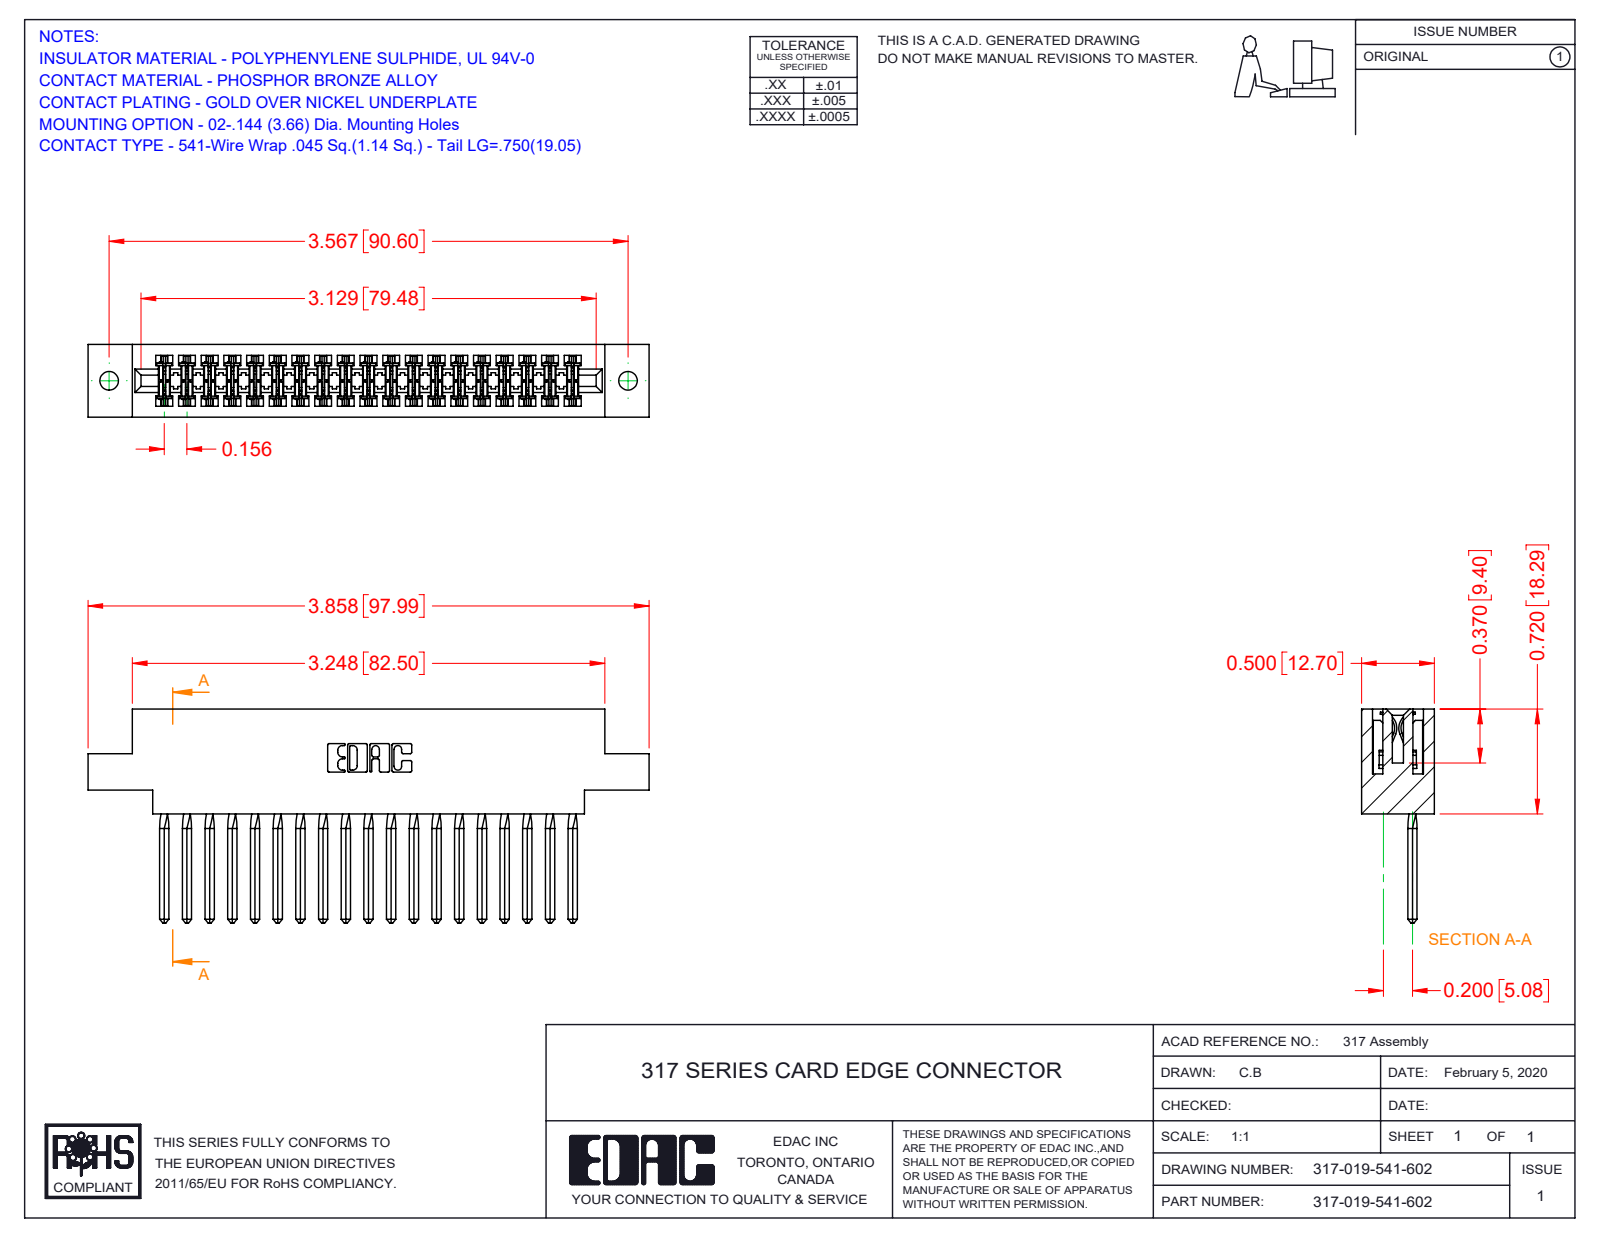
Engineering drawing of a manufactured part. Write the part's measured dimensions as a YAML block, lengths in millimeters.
part_name: "317 Part_.144 Dia; 317-290-002_541; 317-019-541-602"
step_written_by: "SolidWorks 2016 (CONFIG_CONTROL_DESIGN)"
units: millimeters
bodies: {solids: 20, faces: 2990, planar: 2414, cylindrical: 500, other: 76}
overall_size: [98, 37.3, 12.7]
volume: 15100
surface_area: 20370
round_holes:
  - {diameter: 3.3, count: 2}
partial_cylinders:
  - {radius: 0.4, count: 38}
  - {radius: 0.3, count: 22}
  - {radius: 0.2, count: 6}
  - {radius: 0.8, count: 6}
  - {radius: 0.7, count: 3}
  - {radius: 2.4, count: 2}
  - {radius: 2.5, count: 2}
  - {radius: 2.8, count: 2}
face_to_face_distances: [12.7, 1.9, 10.8, 2.8, 8.9, 5, 19.6, 5.6, 16.8, 18.3]
hole_center_spacings: [90.6]
